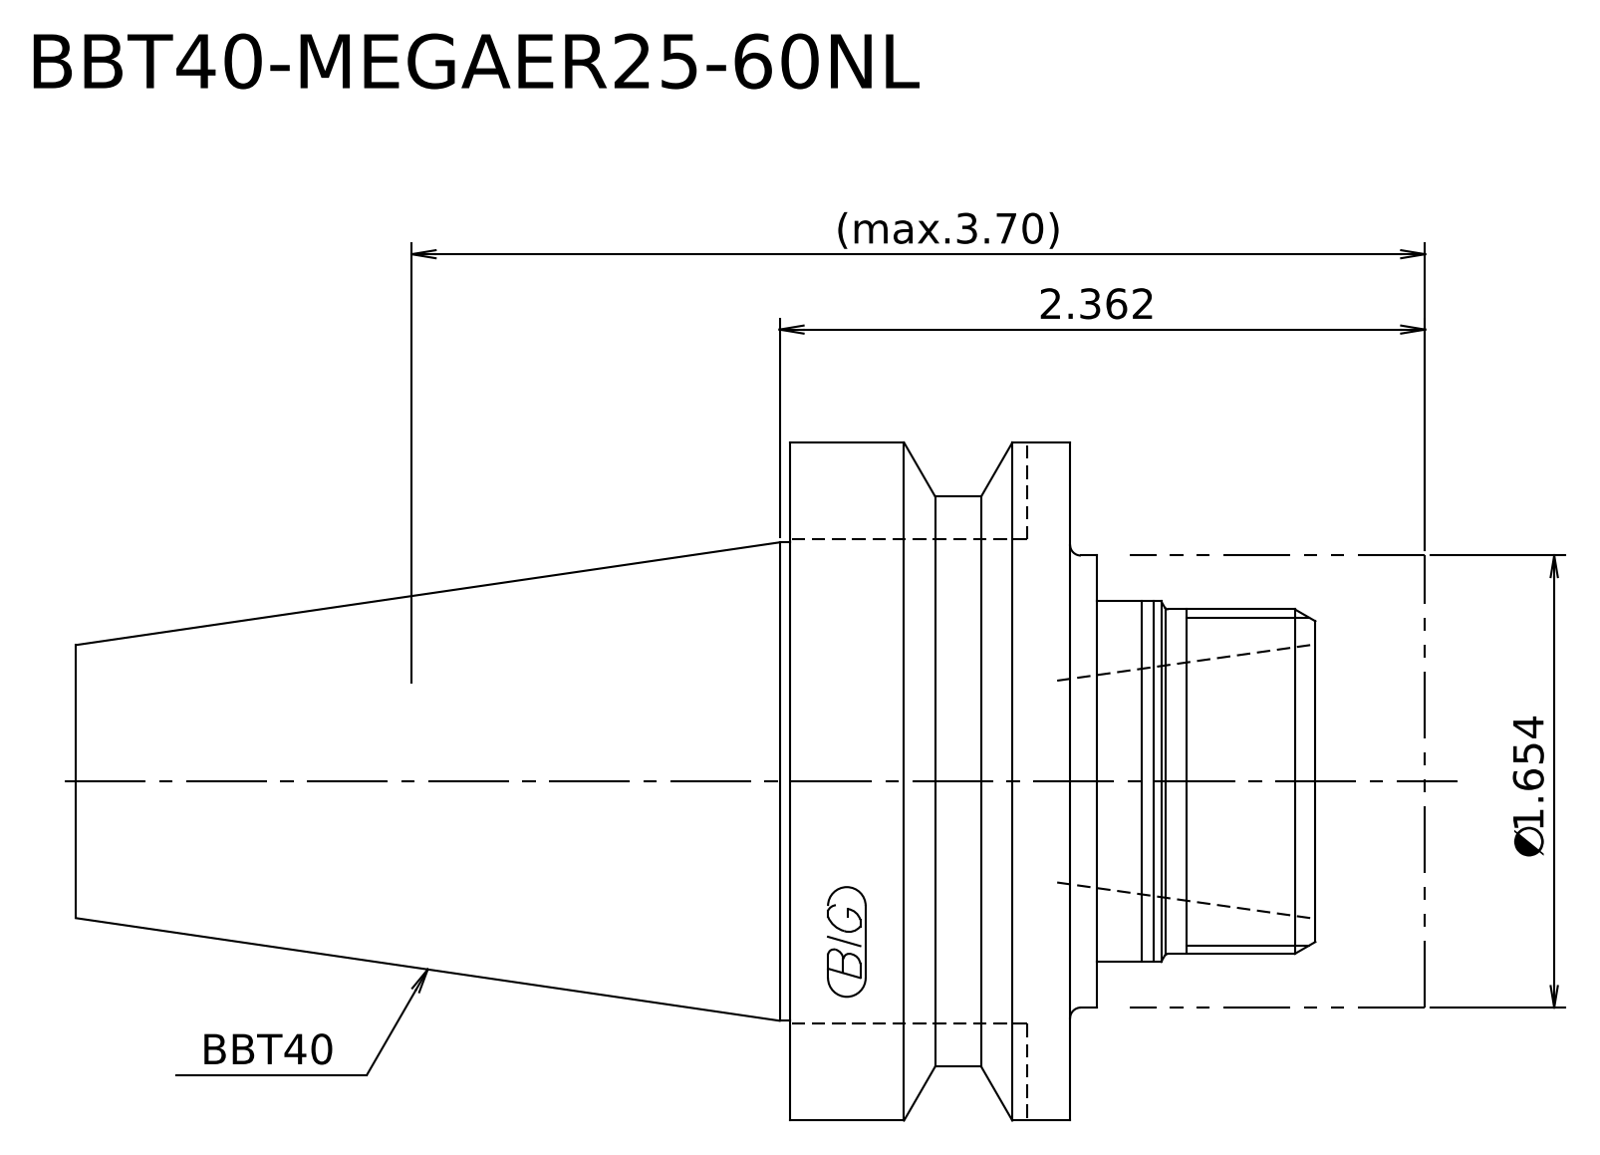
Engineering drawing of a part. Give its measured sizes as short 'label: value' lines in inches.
written by: Kubotek KeyCreator 2011 V10.0.2 (22737) (automotive_design)
unit: in
bodies: 2 solids, 21 faces (7 planar, 8 cylindrical, 6 other)
size: 4.937 × 2.48 × 2.48
volume: 12.11 in³; area: 42.09 in²
bosses: 1× ⌀2.48, 1× ⌀2.087, 1× ⌀1.75, 1× ⌀1.654, 1× ⌀1.319, 1× ⌀1.26
face distances: 1.024, 0.217, 1.24, 1.083, 1.299, 2.323, 0.402, 0.681, 0.898, 1.921
